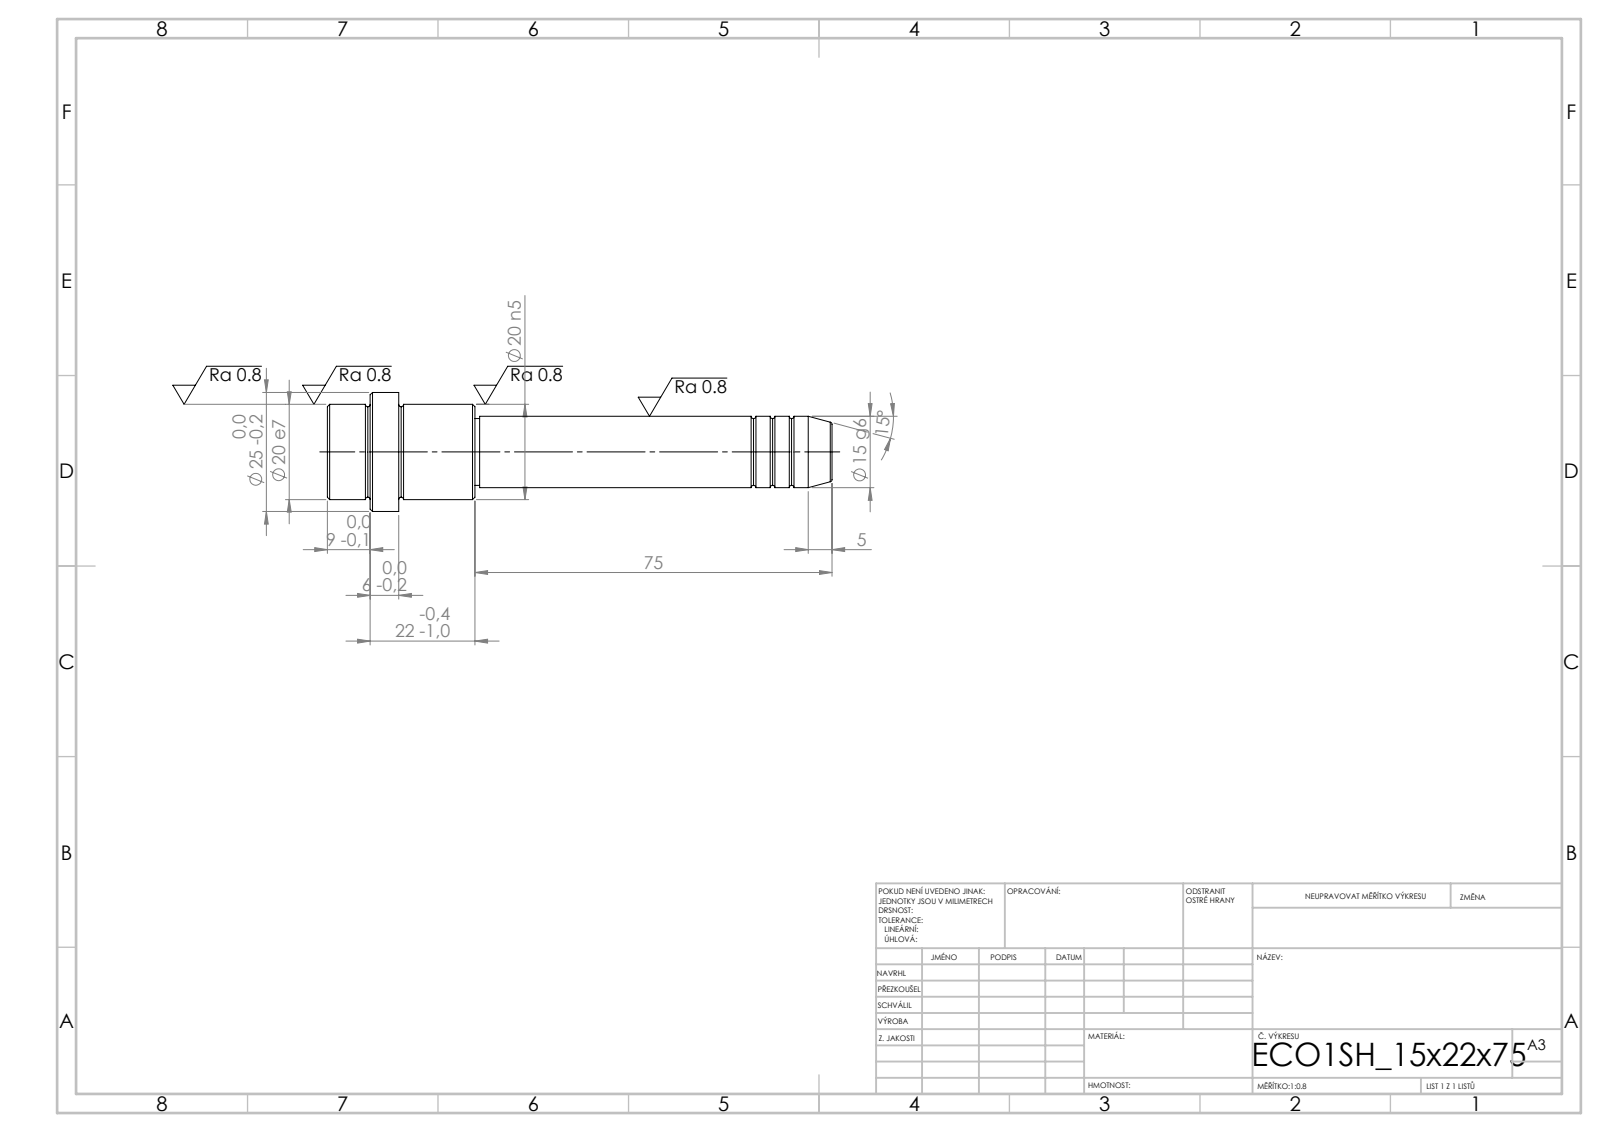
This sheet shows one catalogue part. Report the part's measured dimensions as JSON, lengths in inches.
{"step_written_by": "SolidWorks 2019 (CONFIG_CONTROL_DESIGN)", "units": "inches", "bodies": {"solids": 1, "faces": 52, "planar": 6, "cylindrical": 16, "other": 30}, "overall_size": [4.173, 0.984, 0.984], "volume_in3": 1.449, "surface_area_in2": 10.23, "round_bosses_or_shafts": [[0.984, 1], [0.787, 1], [0.591, 1], [0.551, 1]], "face_to_face_distances": [0.591, 0.236, 0.354, 0.63, 0.866, 1.22, 2.953, 3.583, 3.819, 4.173]}
